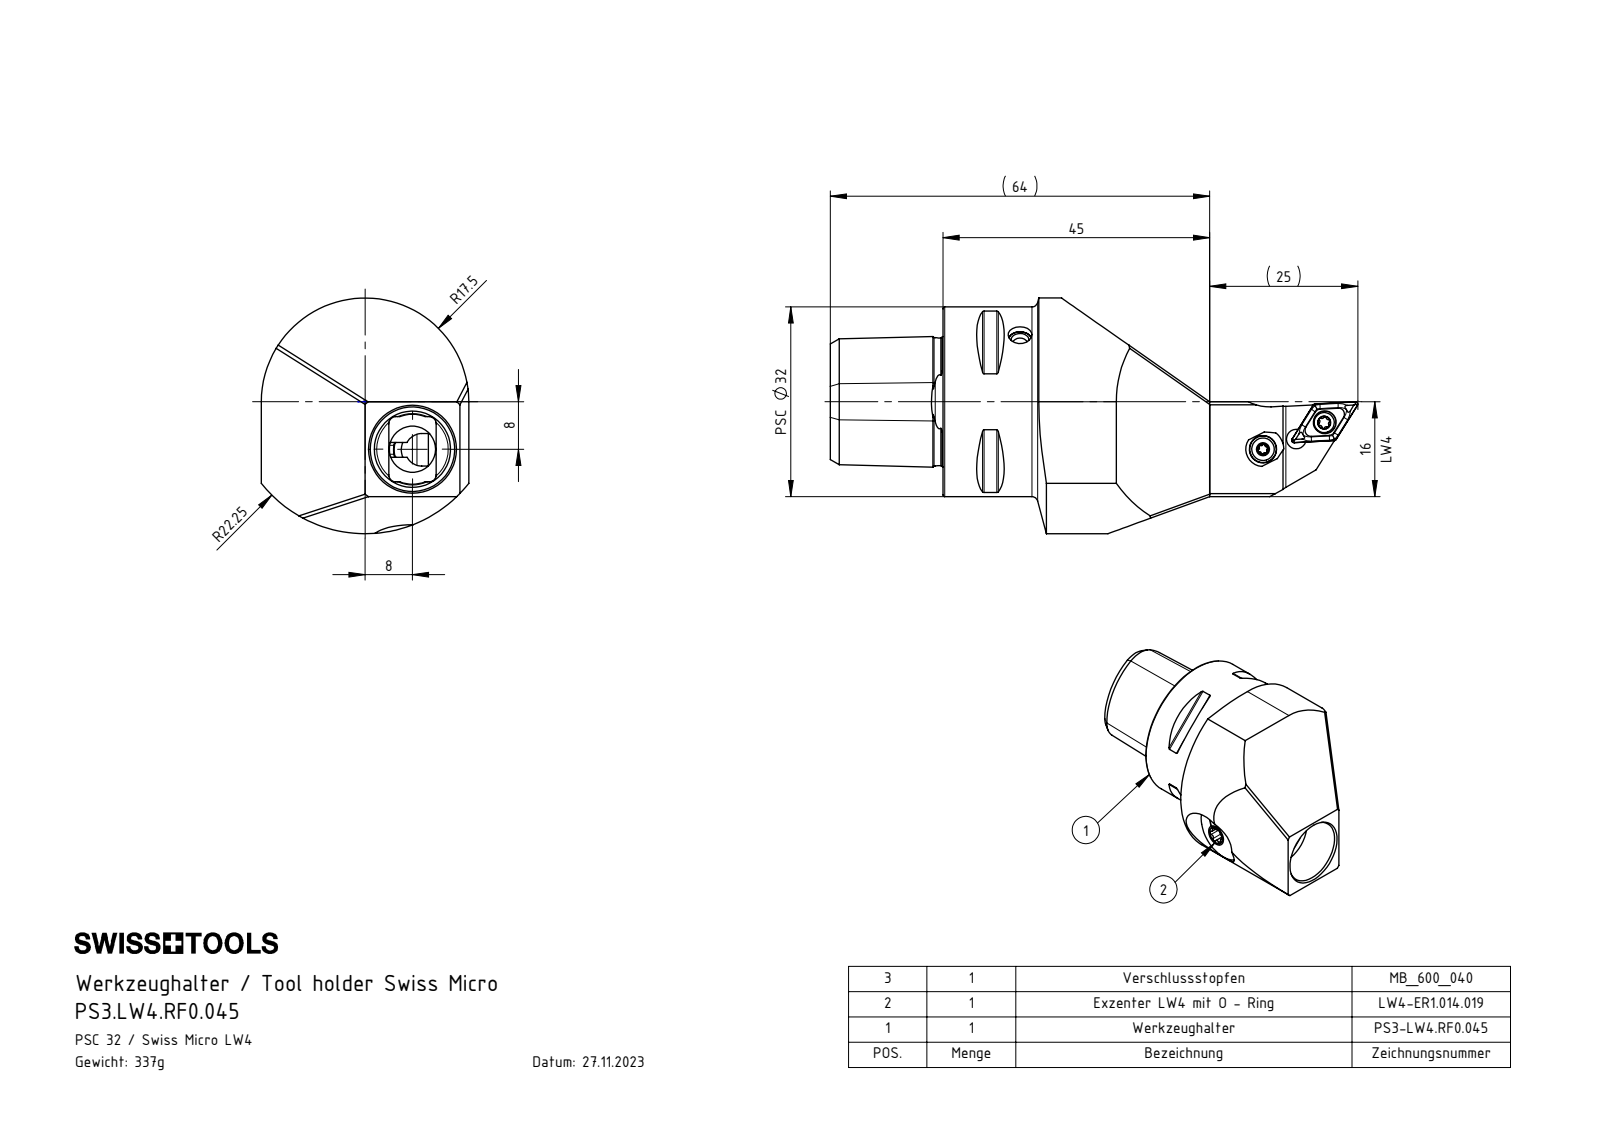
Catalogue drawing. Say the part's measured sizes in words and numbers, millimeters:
The part is named "LW4-ER1.014.019; PS3.LW4.RF0.045; LW4-ER1.014.019_D_Standard<Wie bearbeitet>; KVT_MB_600_040 (+2 more)". Its 3-D file was written by "SolidWorks 2017 (AUTOMOTIVE_DESIGN)". It is 6 solids with 327 faces: 70 planar, 98 cylindrical and 159 other. Overall it measures 64 by 39.75 by 35 millimeters. Its volume is 37 204 cubic millimeters and its surface area 11 935 square millimeters. Round holes: 2 of diameter 3.3, 2 of diameter 4, 1 of diameter 1, 1 of diameter 2.85, 1 of diameter 3, 1 of diameter 3.6, 1 of diameter 7.8, 1 of diameter 10.2, 1 of diameter 12.86, 1 of diameter 14, 1 of diameter 15, 1 of diameter 16.5. Round bosses or shafts: 1 of diameter 32, 1 of diameter 12, 1 of diameter 10.2, 1 of diameter 4. Partial cylindrical surfaces (rounded edges, fillets, slot ends): 8 of radius 0.3, 6 of radius 0.4, 6 of radius 0.69, 4 of radius 1.2, 2 of radius 2.75, 1 of radius 3, 1 of radius 4.1, 1 of radius 4.15. The main face-to-face distances are 35, 19, 64, 45, 12.01, 13.2, 28.3, 1.1, 12.1, 1.4. The hole center spacings are 11.31, 17.
